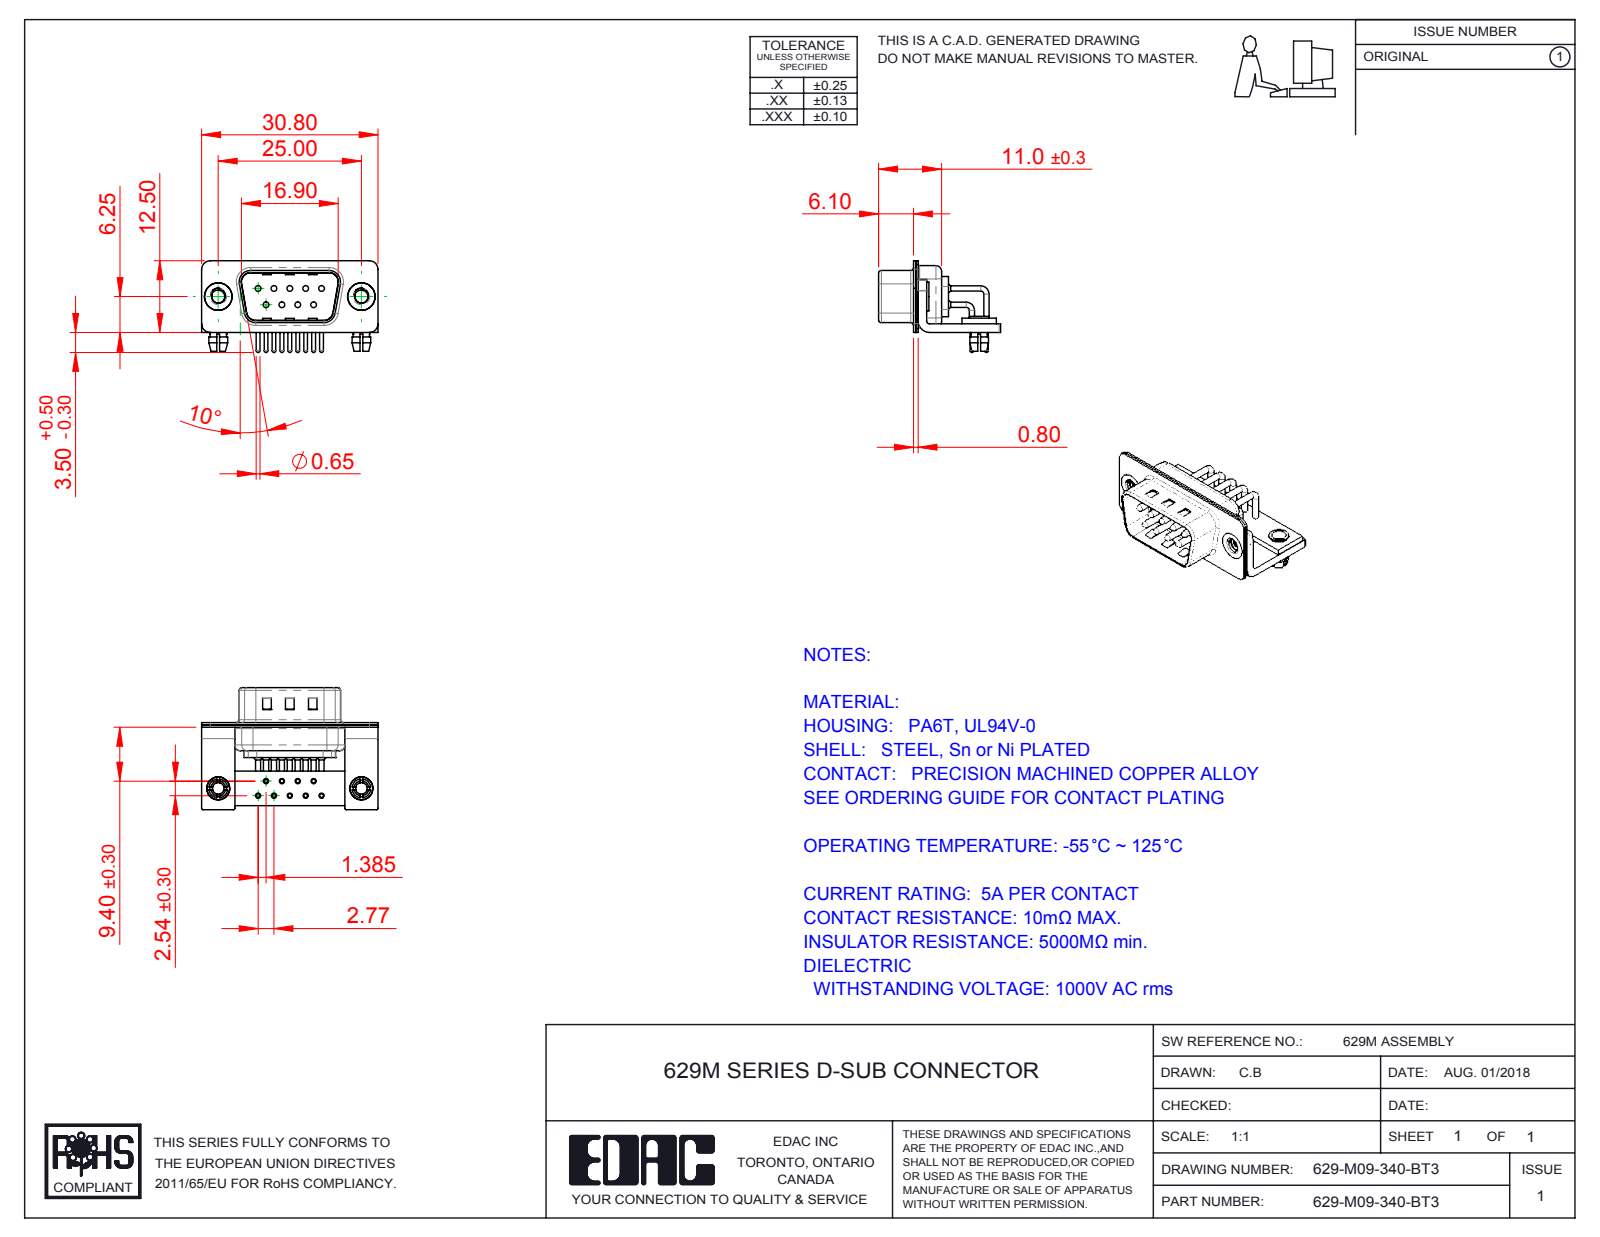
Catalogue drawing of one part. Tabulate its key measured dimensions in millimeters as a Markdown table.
| quantity | value |
| --- | --- |
| part name | 629M Stabilizer Board_09 Contacts; 629M Stabilizer Bracket; 629M 4-40 Threaded Rivet_Stabilizer; 629M Contact Row 2 (+6 more) |
| STEP written by | SolidWorks 2016 (CONFIG_CONTROL_DESIGN) |
| units | millimeters |
| bodies | 19 solids, 1454 faces (757 planar, 525 cylindrical, 172 other) |
| overall size | 30.8 × 21.3 × 16 |
| volume | 1 856 mm³ |
| surface area | 5 184 mm² |
| round holes (diameter × count) | 2 × 11, 0.9 × 9, 1 × 9, 1.7 × 9, 2.26 × 2, 2.5 × 2, 3.2 × 2, 4 × 2, 4.8 × 2 |
| round bosses / shafts (diameter × count) | 1.5 × 9, 0.9 × 9, 0.65 × 9, 5 × 2, 4.9 × 2, 4 × 2, 3.4 × 2, 3.3 × 2 |
| partial cylindrical surfaces (radius × count) | 0.25 × 16, 1.5 × 16, 2 × 13, 0.5 × 9, 1.01 × 9, 1.6 × 8, 0.6 × 4, 0.65 × 4 |
| main face-to-face distances | 0.4, 1.5, 0.8, 0.85, 1.25, 1.9, 1, 2.5, 10.4, 9.55 |
| hole center spacings | 2.77, 5.54, 3.16, 4.87, 8.31, 2.89, 2.9, 5.03 |
